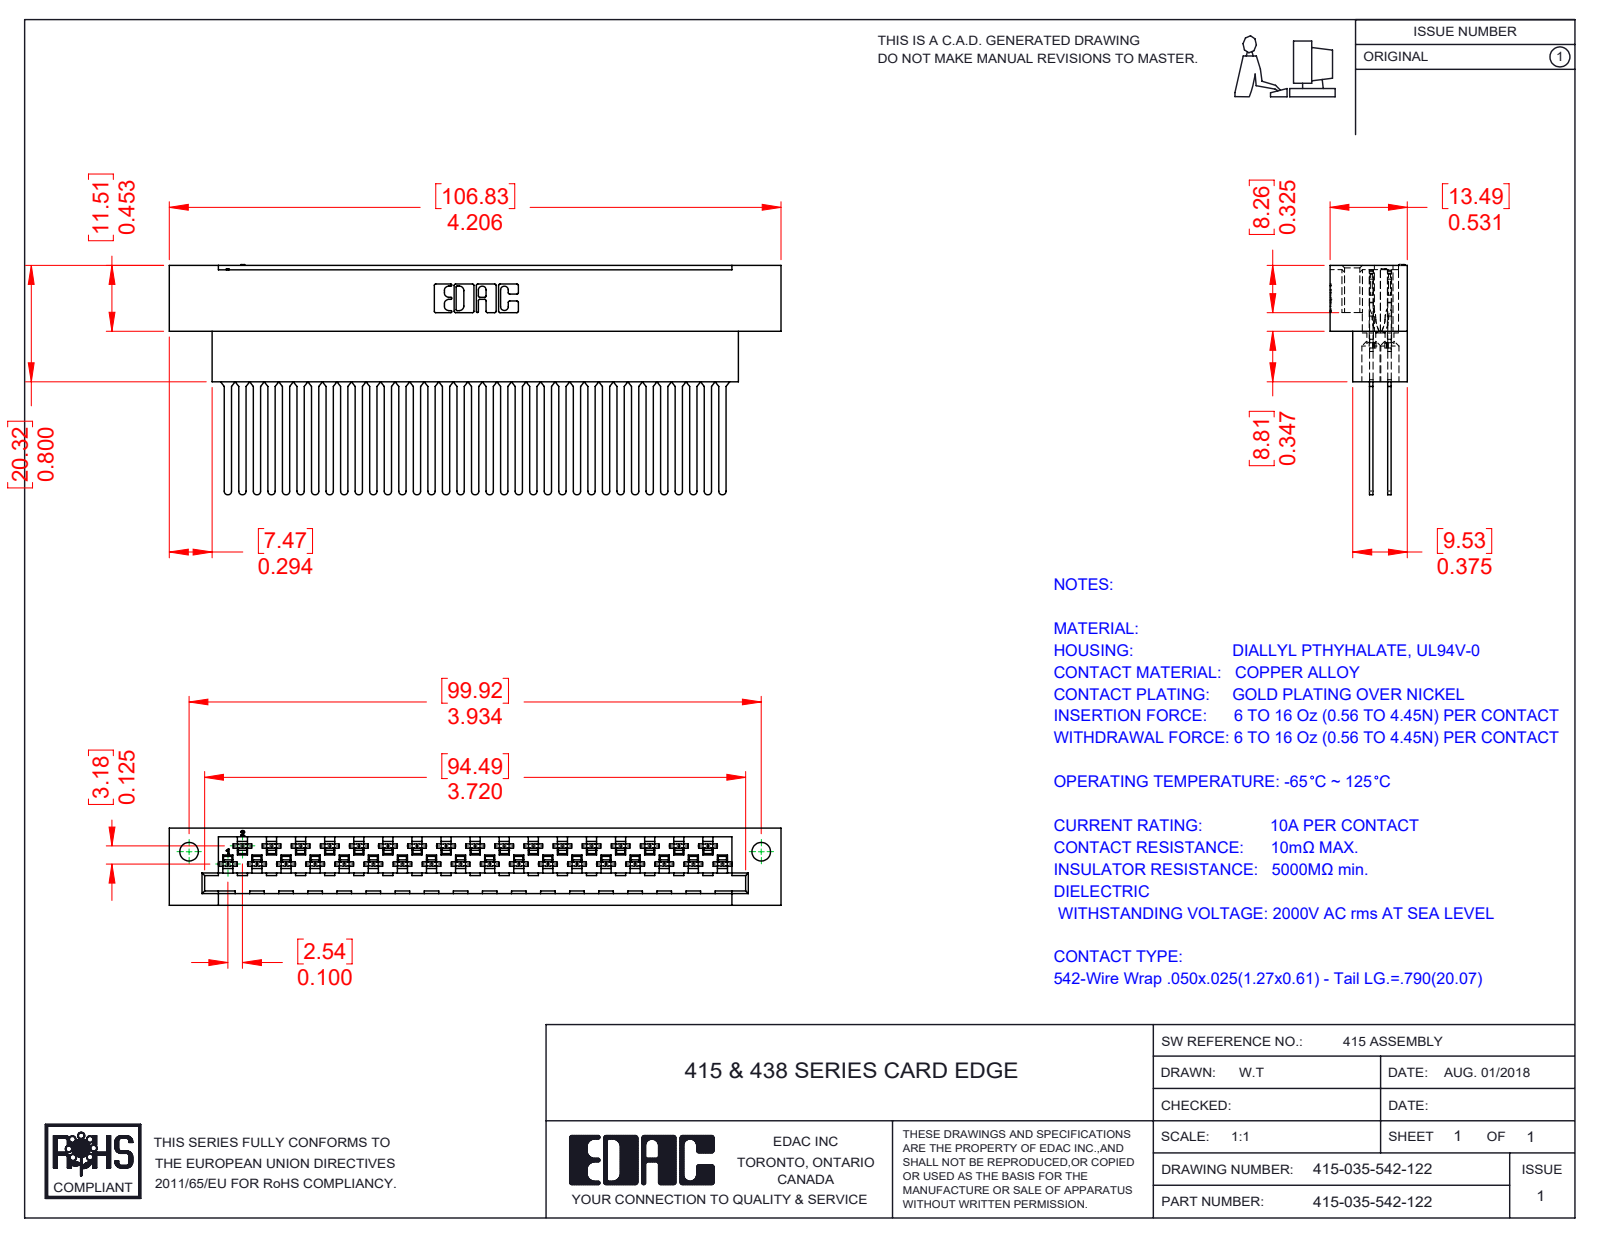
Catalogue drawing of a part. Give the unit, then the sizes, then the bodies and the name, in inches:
Units: inches
Overall size (bounding box): 4.206 × 1.581 × 0.531
Round holes (diameter × count): ⌀0.05 ×35, ⌀0.13 ×35, ⌀0.128 ×2
Partial cylindrical surfaces — rounded edges, fillets, slot ends (radius × count): R0.012 ×140, R0.022 ×140, R0.007 ×70, R0.008 ×70, R0.016 ×70, R0.08 ×70, R0.025 ×35, R0.01 ×22
Main face-to-face distances: 0.125, 0.024, 0.295, 0.26, 0.236, 0.05, 0.074, 0.149, 0.111, 0.135
Hole centre spacings: 0.2, 0.4, 0.6, 0.8, 1, 1.2, 1.4, 0.1
Volume: 1.091 in³ · Surface area: 37.67 in²
Bodies: 36 solids, 3574 faces (2283 planar, 954 cylindrical, 337 other)
Part name (STEP PRODUCT): 415-210-001_415-210-035-122; 516-290-001_542; 415-035-542-122
STEP written by: SolidWorks 2016 (CONFIG_CONTROL_DESIGN)
